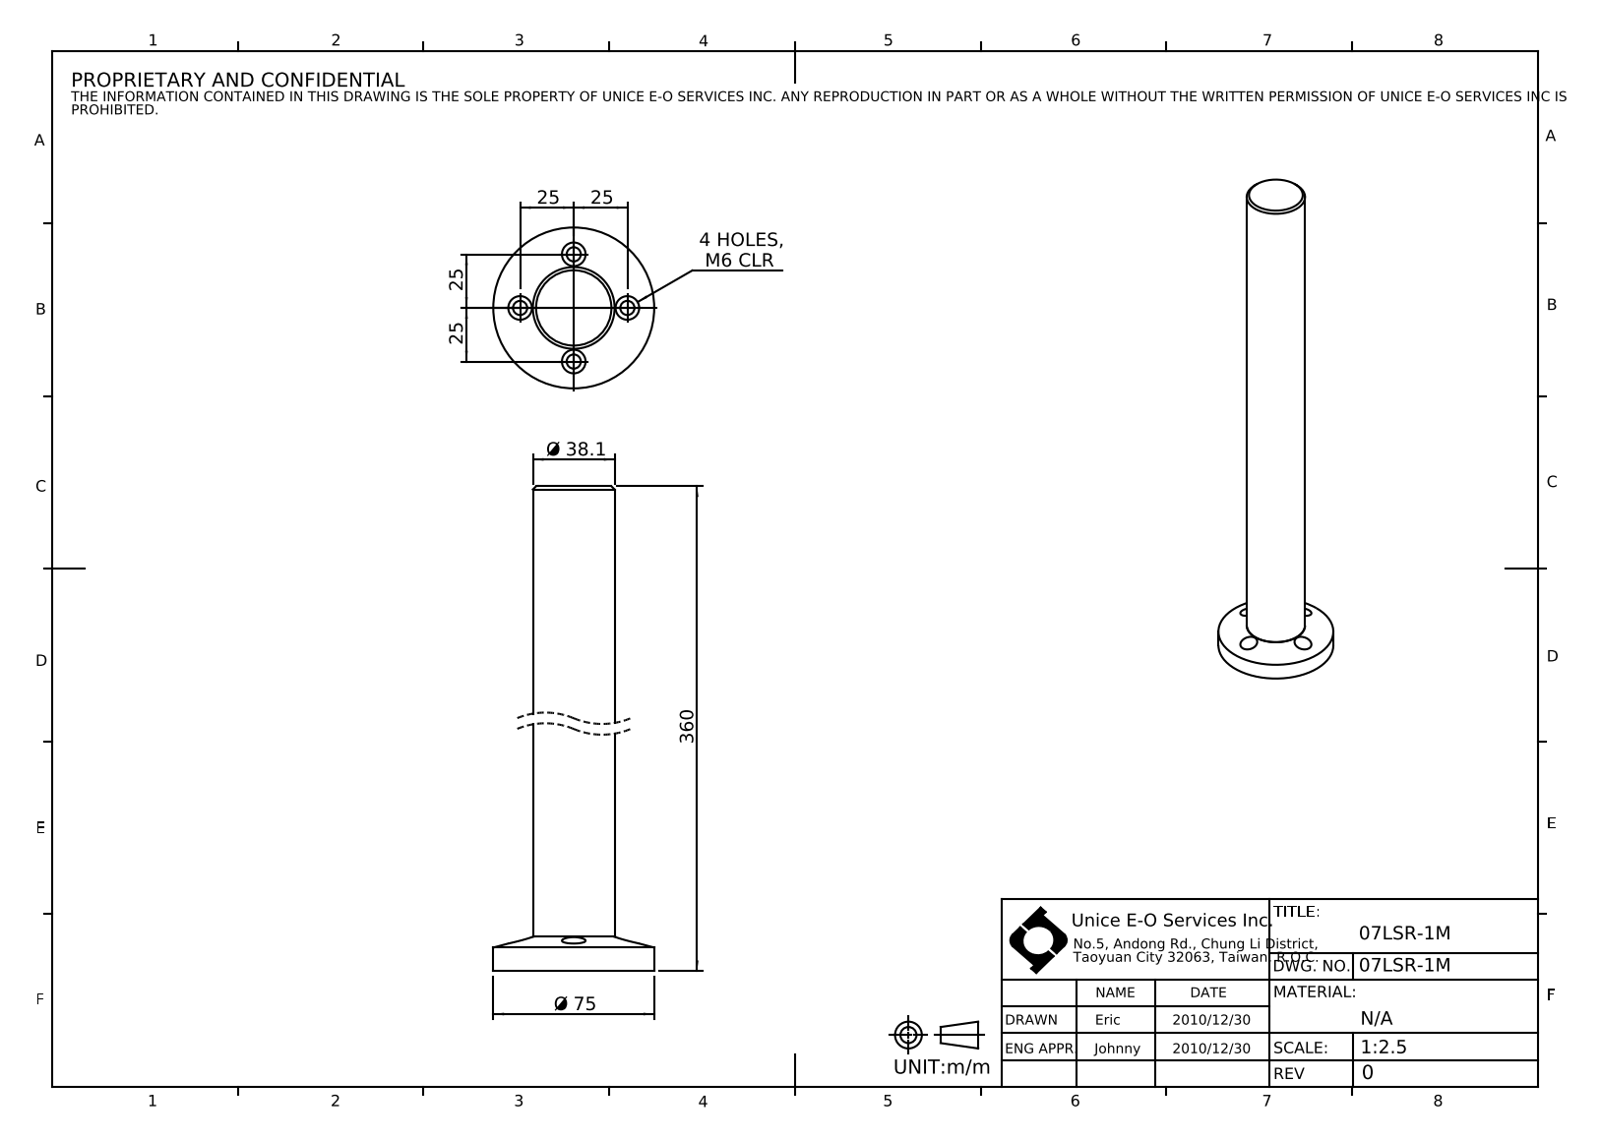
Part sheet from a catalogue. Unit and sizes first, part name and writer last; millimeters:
Units: millimetres
Overall size (bounding box): 360 × 75 × 75
Round holes (diameter × count): ⌀6.6 ×5, ⌀11 ×5, ⌀5 ×1, ⌀25 ×1
Round bosses / shafts (diameter × count): ⌀75 ×1, ⌀38.1 ×1
Main face-to-face distances: 16, 360, 344, 3, 13, 347, 12.7, 3.3, 347.3, 9
Hole centre spacings: 25, 35.36, 50
Volume: 447 892 mm³ · Surface area: 57 354 mm²
Bodies: 2 solids, 47 faces (11 planar, 30 cylindrical, 6 other)
Part name (STEP PRODUCT): 07LSR-1M
STEP written by: SolidWorks 2016 (CONFIG_CONTROL_DESIGN)
